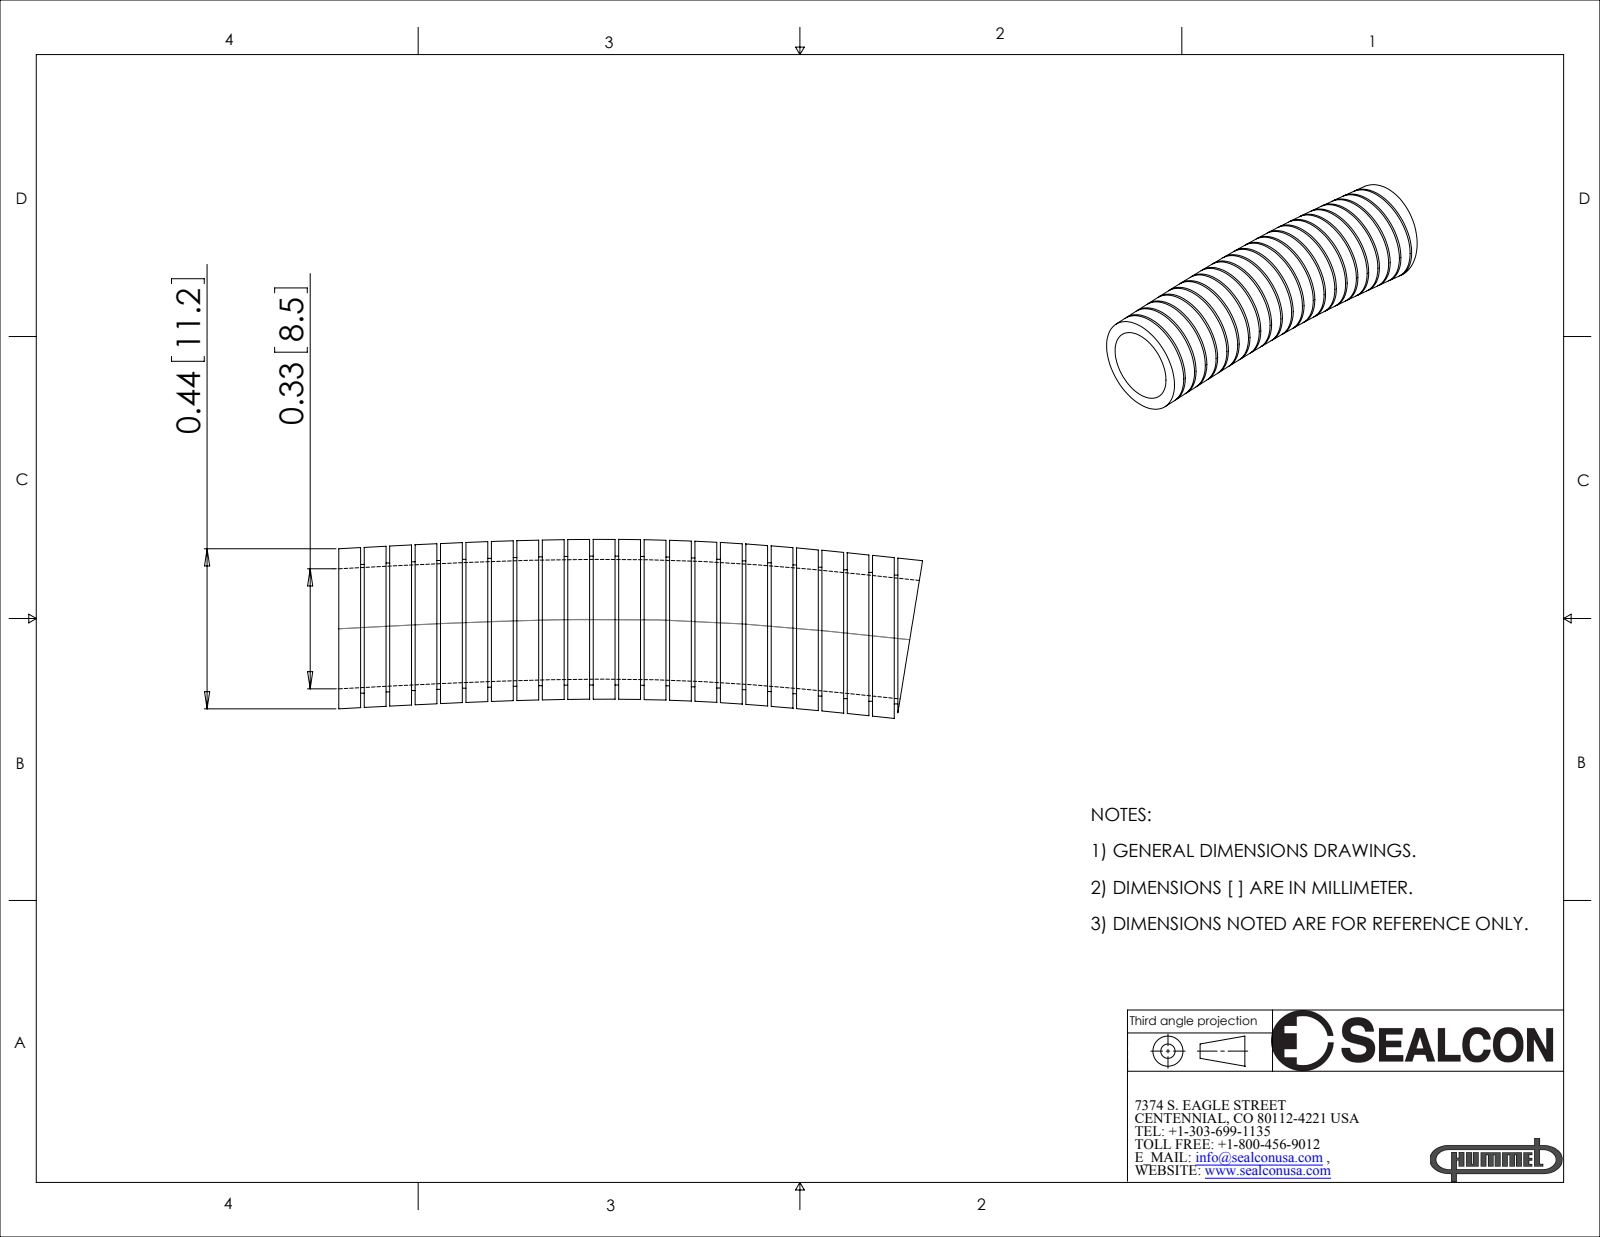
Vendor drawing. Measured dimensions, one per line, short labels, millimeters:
name: SM-1013-HY
written by: SolidWorks 2007 (AUTOMOTIVE_DESIGN)
unit: mm
bodies: 1 solid, 139 faces (46 planar, 44 cylindrical, 49 other)
size: 40.8 × 12.5 × 11.2
volume: 1 500 mm³; area: 4 023 mm²
bosses: 20× ⌀9
face distances: 1.8, 1.5, 3.5, 5.3, 3.3, 2, 5.1, 7.1, 10.6, 8.9
